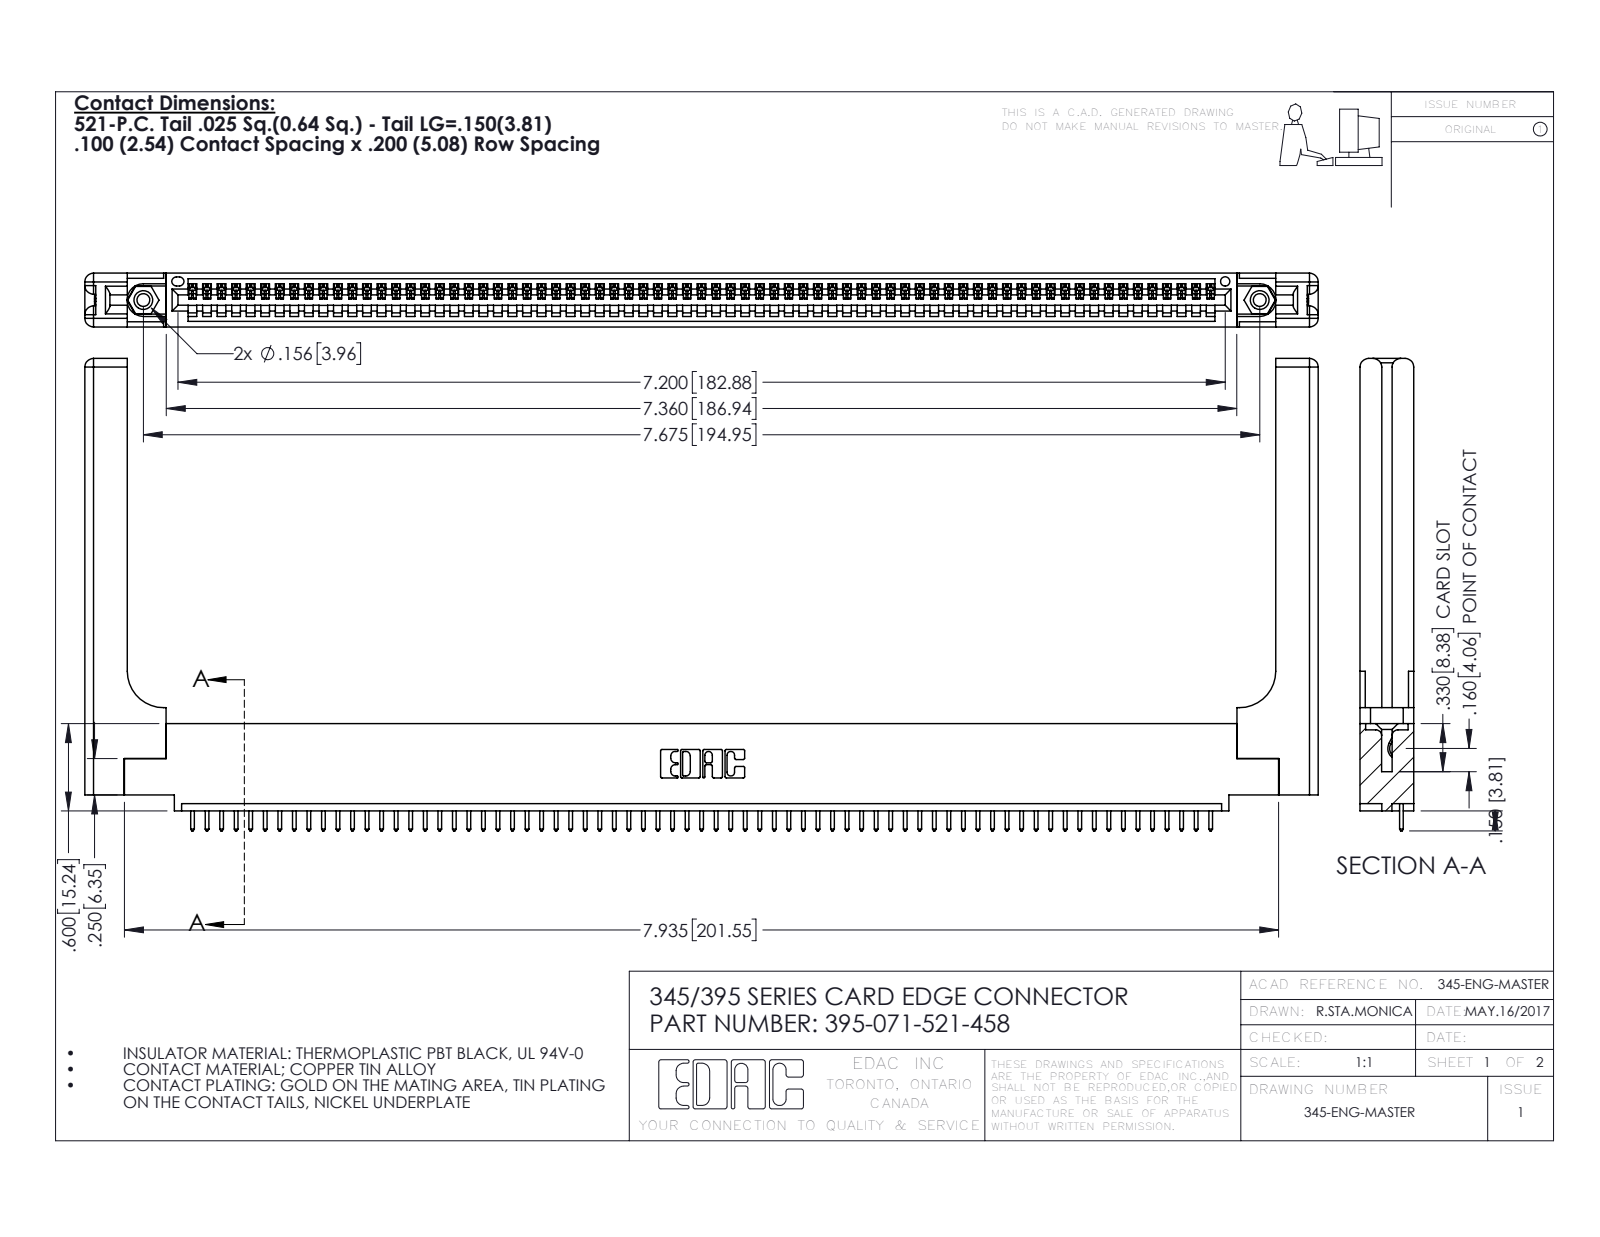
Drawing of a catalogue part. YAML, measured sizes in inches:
part_name: "395-071-521-458; 345-250-001_345-250-001-102; 345 Part_0.110 Offset - 0.156 Dia-TH; 345-220-058_345-220-058 (+1 more)"
step_written_by: "SolidWorks 2016 (CONFIG_CONTROL_DESIGN)"
units: inches
bodies: {solids: 76, faces: 4504, planar: 3072, cylindrical: 1372, other: 60}
overall_size: [8.479, 3.247, 0.37]
volume: 1.765
surface_area: 49.79
round_holes:
  - {diameter: 0.089, count: 2}
  - {diameter: 0.125, count: 2}
  - {diameter: 0.156, count: 2}
  - {diameter: 0.064, count: 1}
round_bosses_or_shafts:
  - {diameter: 0.155, count: 2}
partial_cylinders:
  - {radius: 0.006, count: 142}
  - {radius: 0.01, count: 142}
  - {radius: 0.01, count: 22}
  - {radius: 0.06, count: 16}
  - {radius: 0.007, count: 6}
  - {radius: 0.031, count: 6}
  - {radius: 0.026, count: 3}
  - {radius: 0.03, count: 2}
face_to_face_distances: [0.072, 0.298, 0.37, 0.098, 0.272, 0.025, 0.2, 0.225, 0.148, 0.15]
hole_center_spacings: [0.27, 7.439, 7.675]
